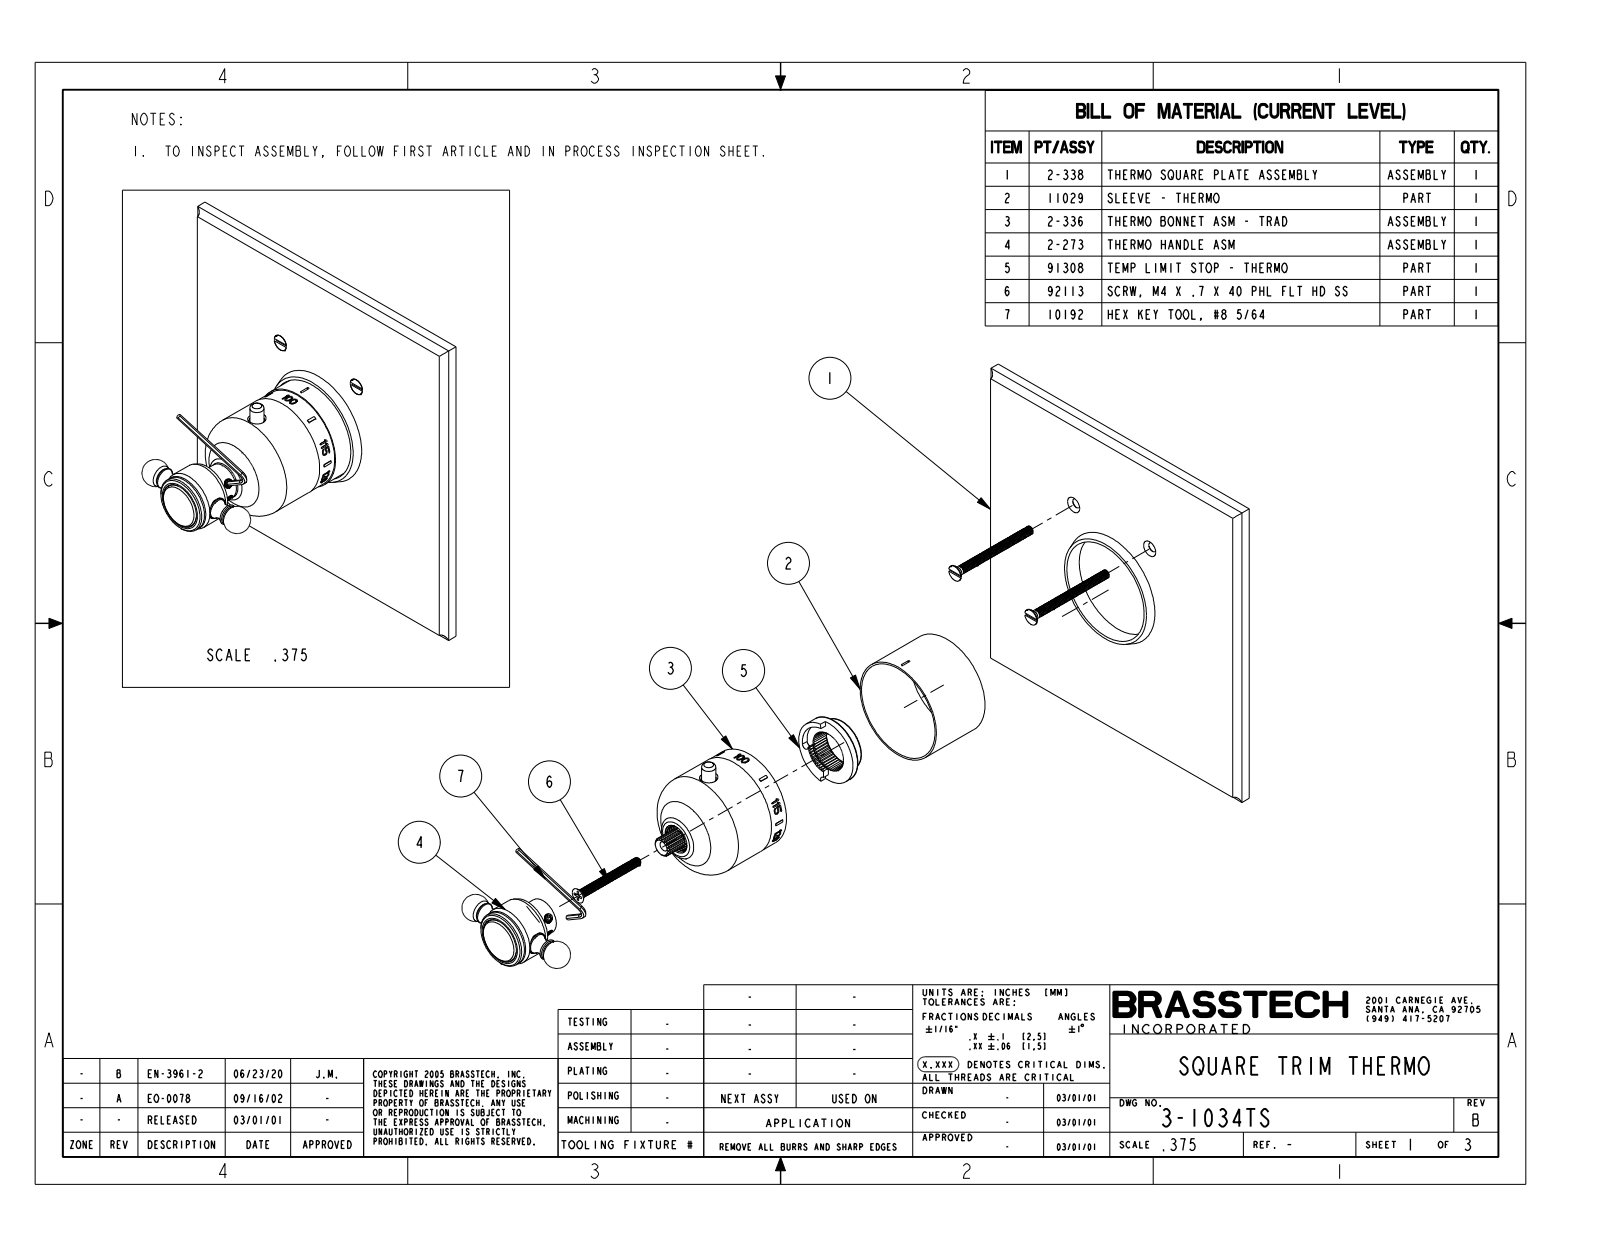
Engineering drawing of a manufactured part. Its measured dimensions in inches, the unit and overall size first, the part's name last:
Units: inches
Overall size (bounding box): 6.5 × 6.5 × 3.979
Round holes (diameter × count): ⌀0.41 ×1
Round bosses / shafts (diameter × count): ⌀1.97 ×1, ⌀1.94 ×1, ⌀1.929 ×1, ⌀1.115 ×1, ⌀1.055 ×1, ⌀0.687 ×1, ⌀0.392 ×1, ⌀0.37 ×1
Partial cylindrical surfaces — rounded edges, fillets, slot ends (radius × count): R0.125 ×4, R0.969 ×1
Main face-to-face distances: 0.313, 6.5, 2.748, 2.435, 2.779, 2.466, 0.031, 0.854, 0.541, 1.894
Volume: 20.49 in³ · Surface area: 111 in²
Bodies: 1 solid, 442 faces (341 planar, 49 cylindrical, 52 other)
Part name (STEP PRODUCT): 3-1034TS
STEP written by: CREO PARAMETRIC BY PTC INC, 2018400 (CONFIG_CONTROL_DESIGN)
